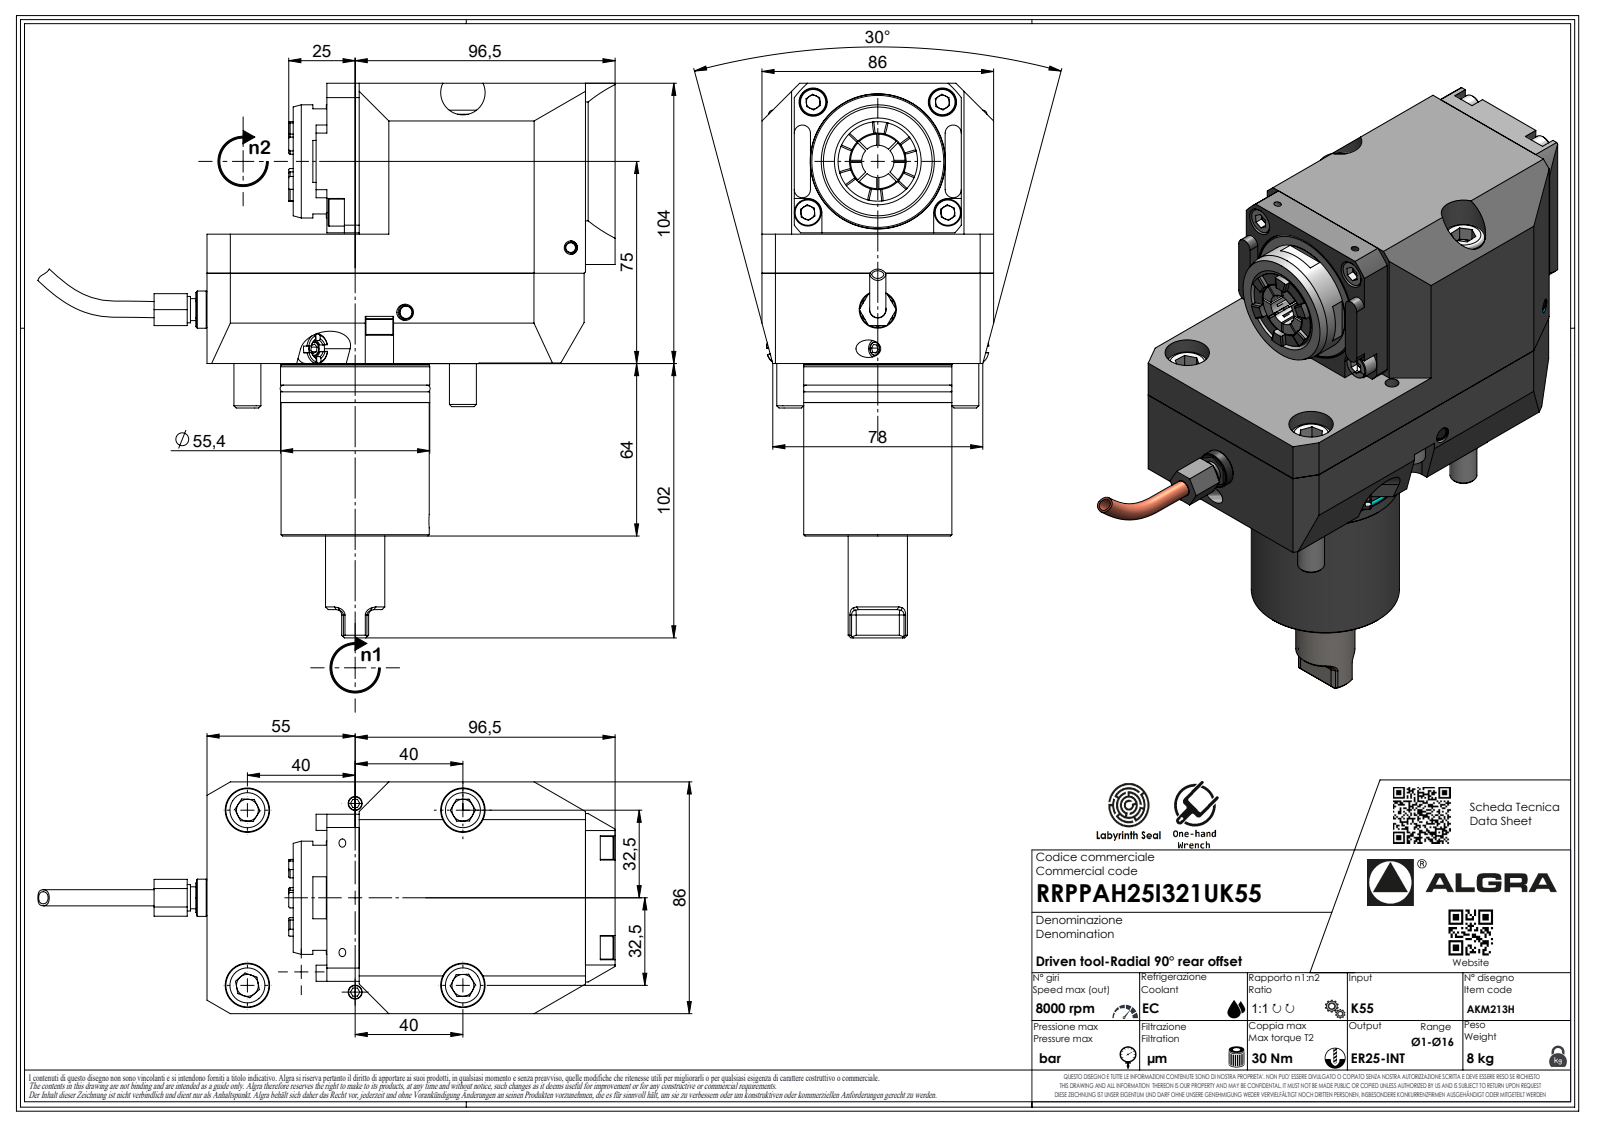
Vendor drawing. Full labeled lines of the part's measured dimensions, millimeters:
Part name (STEP PRODUCT): RRPPAH25I321UK55
STEP written by: SolidWorks 2023 (AUTOMOTIVE_DESIGN)
Units: millimetres
Bodies: 1 solid, 598 faces (374 planar, 100 cylindrical, 124 other)
Overall size (bounding box): 214.29 × 205.8 × 86
Volume: 1 153 000 mm³ · Surface area: 94 622 mm²
Round holes (diameter × count): ⌀16.5 ×3, ⌀2.1 ×1, ⌀5 ×1, ⌀8.57 ×1, ⌀47 ×1, ⌀47.2 ×1
Round bosses / shafts (diameter × count): ⌀10 ×4, ⌀16 ×2, ⌀55.39 ×1, ⌀55 ×1, ⌀54.99 ×1, ⌀51.5 ×1, ⌀42 ×1, ⌀25 ×1
Partial cylindrical surfaces — rounded edges, fillets, slot ends (radius × count): R35 ×8, R0.33 ×7, R0.52 ×7, R3.7 ×7, R2 ×6, R3 ×4, R5.25 ×4, R4.5 ×2
Main face-to-face distances: 86, 104, 56, 48, 151.5, 11.5, 140, 44.5, 95.5, 107
Hole centre spacings: 51.54, 38.94, 65, 77.28, 89.74
